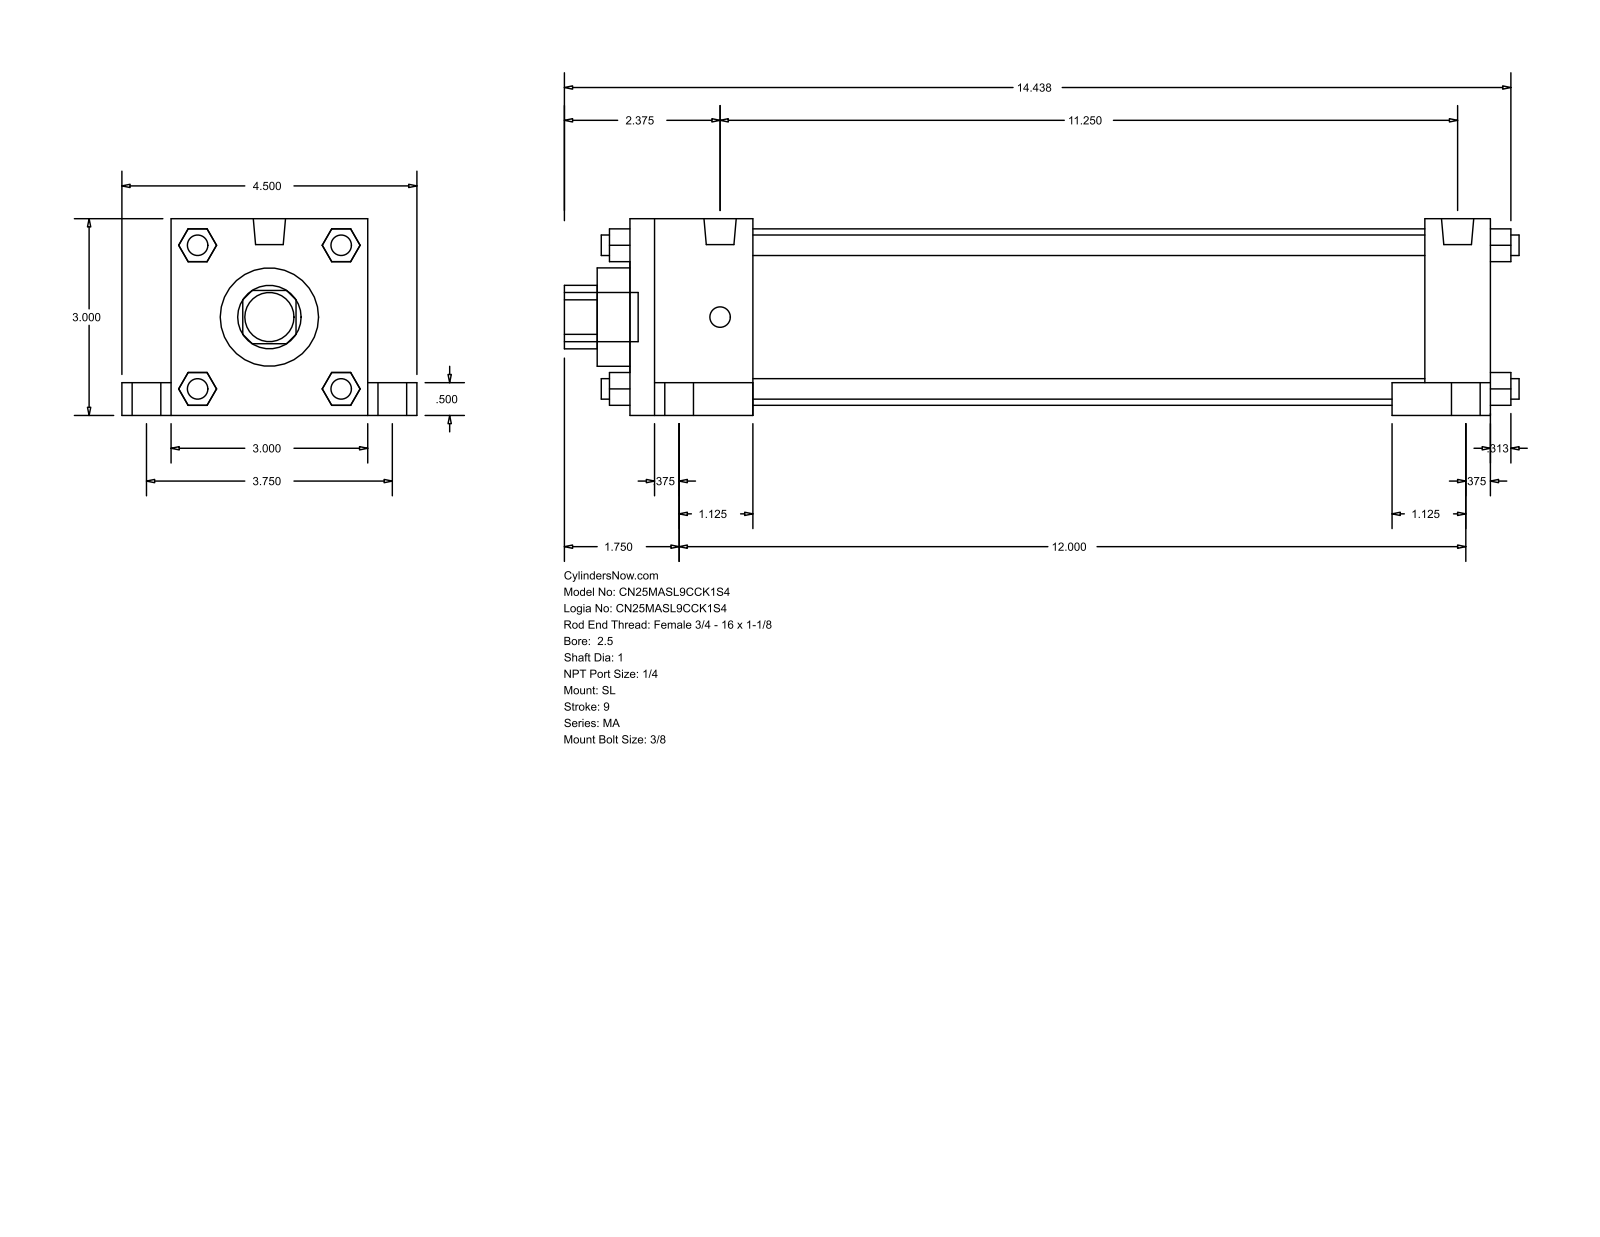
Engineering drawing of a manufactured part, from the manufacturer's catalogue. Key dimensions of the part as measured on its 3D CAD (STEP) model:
Part name (STEP PRODUCT): MA_SL__0250_1
STEP written by: GSSL Pune (CONFIG_CONTROL_DESIGN)
Units: millimetres
Bodies: 0 solids, 148 faces (112 planar, 36 cylindrical, 0 other)
Overall size (bounding box): 369.89 × 114.3 × 76.2
Round holes (diameter × count): ⌀25.4 ×1, ⌀38.1 ×1, ⌀68.33 ×1
Round bosses / shafts (diameter × count): ⌀7.94 ×8, ⌀17.46 ×4, ⌀11.11 ×4, ⌀12.49 ×2, ⌀19.05 ×1
Partial cylindrical surfaces — rounded edges, fillets, slot ends (radius × count): R12.29 ×1
Main face-to-face distances: 76.2, 333.37, 12.7, 260.35, 25.39, 47.63, 285.74, 307.98, 19.05, 95.25
